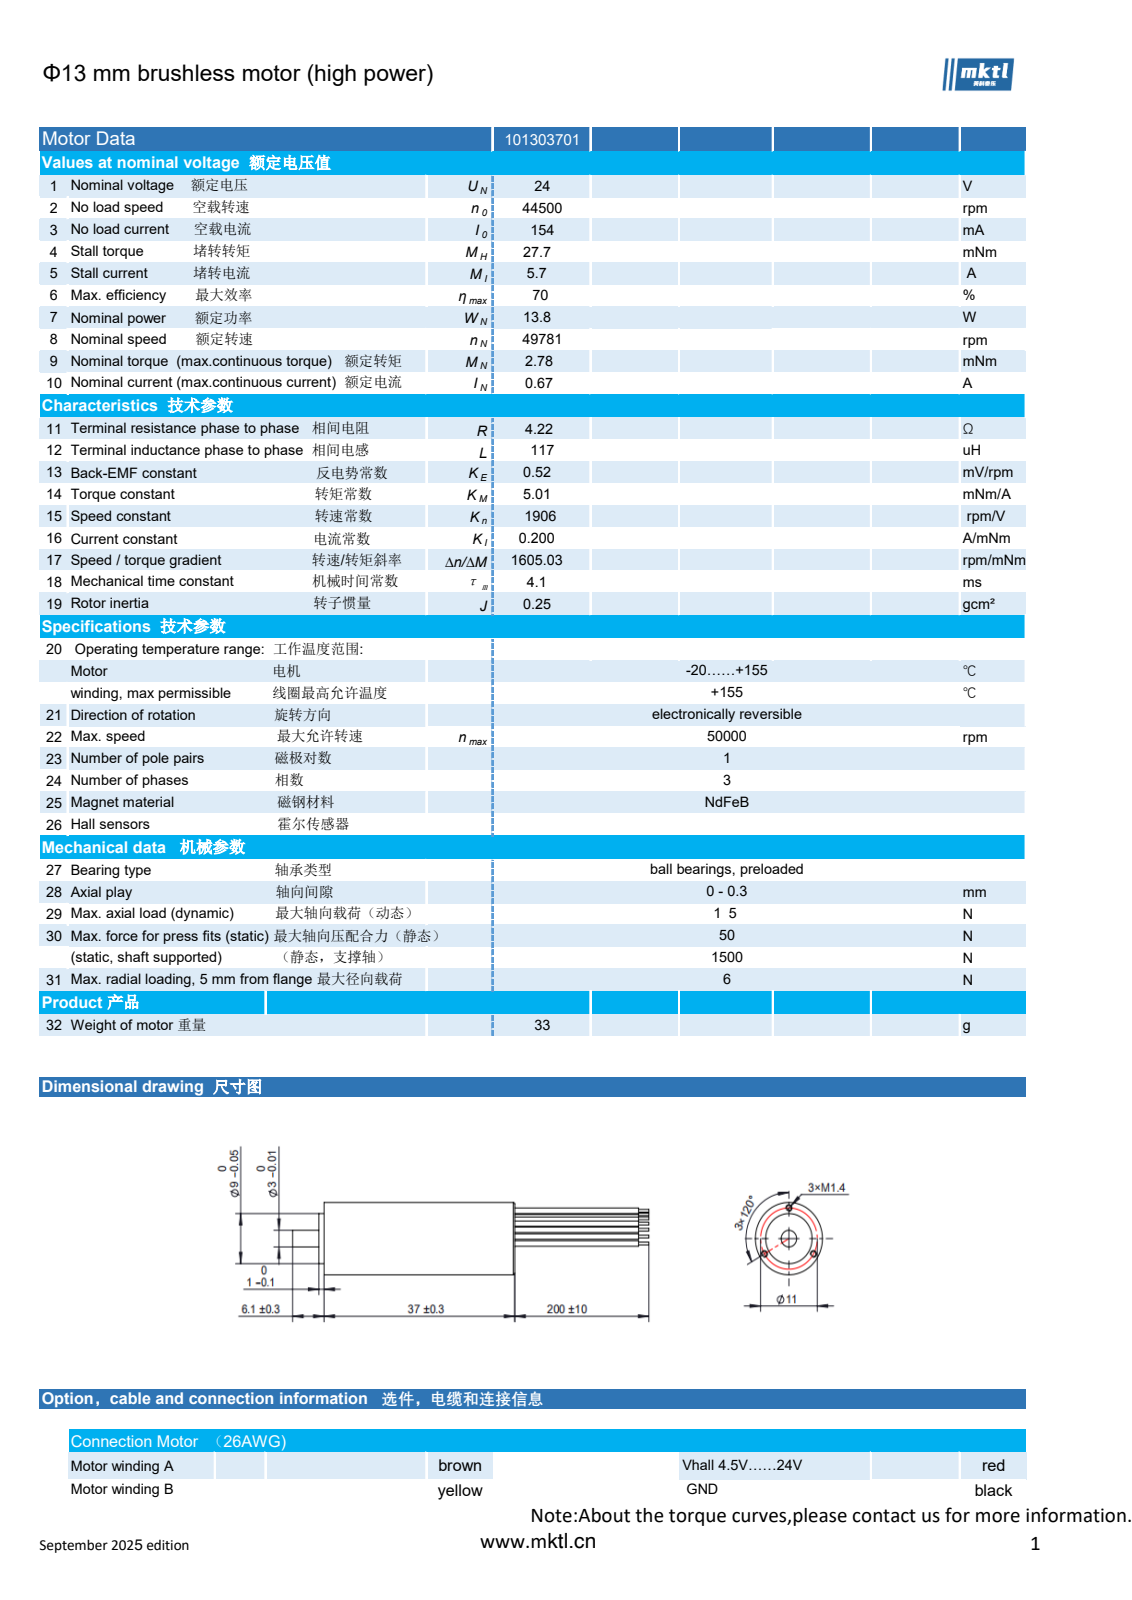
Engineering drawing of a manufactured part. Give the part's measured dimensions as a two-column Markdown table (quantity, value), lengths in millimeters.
| quantity | value |
| --- | --- |
| part name | 101303701 |
| STEP written by | SolidWorks 2018 (CONFIG_CONTROL_DESIGN) |
| units | millimeters |
| bodies | 1 solid, 79 faces (21 planar, 50 cylindrical, 8 other) |
| overall size | 69.1 × 13 × 13 |
| volume | 5 148 mm³ |
| surface area | 2 552 mm² |
| round holes (diameter × count) | 0.95 × 3 |
| round bosses / shafts (diameter × count) | 1 × 8, 0.5 × 8, 13 × 1, 9 × 1, 3 × 1 |
| partial cylindrical surfaces (radius × count) | 0.75 × 2, 4.25 × 1, 5.75 × 1 |
| main face-to-face distances | 37, 1, 38, 36, 5.1, 6.1, 42.1, 43.1, 67.1, 62 |
| hole center spacings | 9.52 |
